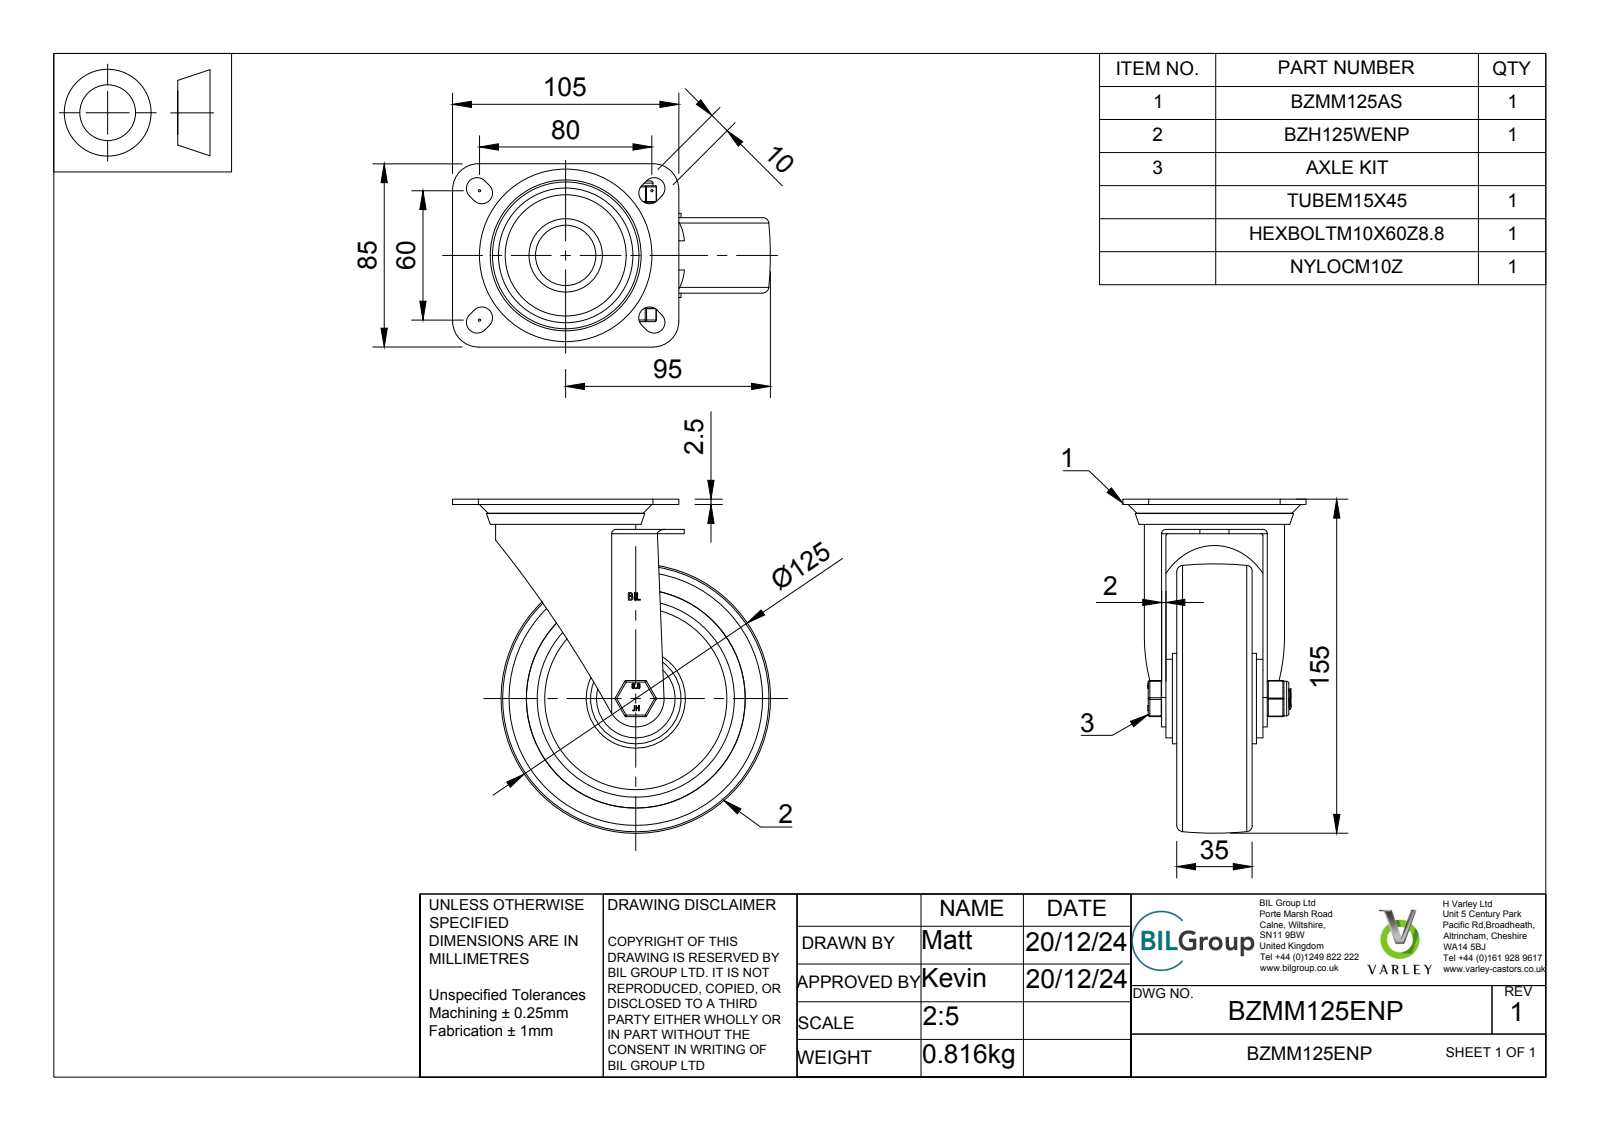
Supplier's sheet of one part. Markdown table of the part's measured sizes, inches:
| quantity | value |
| --- | --- |
| part name | BZMM125ENP v3; BZMM125AS - 2 v2; ZINC PLATED, PRESSED STEEL TOP PLATE; ZINC PLATED, PRESSED STEEL FORKS (+8 more) |
| STEP written by | Autodesk Translation Framework v13.20.0.188 (AP242_MANAGED_MODEL_BASED_3D_ENGINEERING_MIM_LF) |
| units | inches |
| bodies | 9 solids, 349 faces (131 planar, 123 cylindrical, 95 other) |
| overall size | 6.102 × 5.807 × 3.346 |
| volume | 22.18 in³ |
| surface area | 206.8 in² |
| round holes (diameter × count) | 0.394 × 1, 0.402 × 1, 0.406 × 1, 0.472 × 1, 0.606 × 1, 1.102 × 1, 2.402 × 1, 3.602 × 1, 3.996 × 1 |
| round bosses / shafts (diameter × count) | 2.559 × 1, 1.929 × 1, 1.654 × 1, 1.437 × 1, 1.339 × 1, 0.63 × 1, 0.61 × 1, 0.589 × 1 |
| partial cylindrical surfaces (radius × count) | 0.02 × 18, 0.03 × 12, 0.197 × 8, 0.039 × 4, 0.472 × 4, 0.079 × 2, 0.815 × 2, 0.517 × 1 |
| main face-to-face distances | 0.197, 0.079, 0.541, 0.837, 0.276, 0.295, 0.738, 1.033, 1.575, 0.098 |
